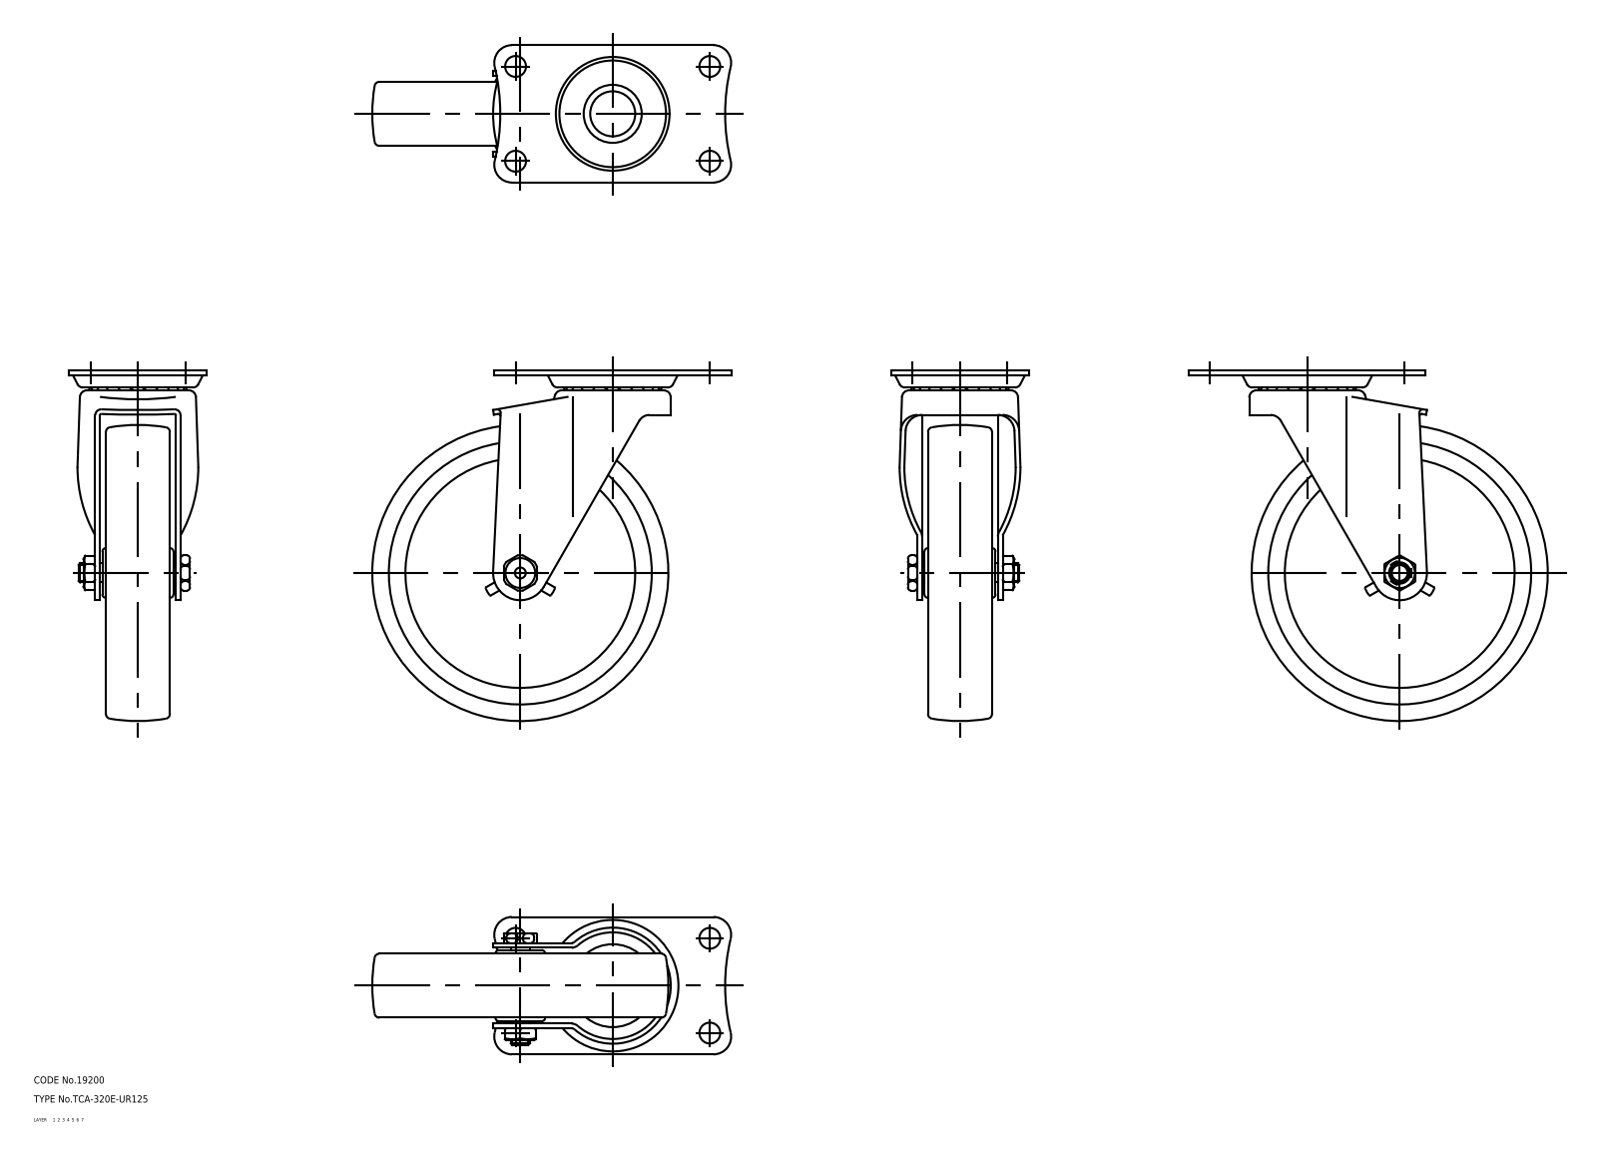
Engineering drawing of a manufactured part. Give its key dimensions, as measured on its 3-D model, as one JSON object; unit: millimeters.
{"part_name": "wheel; mounting plate; main shaft; axle (+1 more)", "step_written_by": "CADfix (AUTOMOTIVE_DESIGN)", "units": "millimeters", "bodies": {"solids": 5, "faces": 372, "planar": 0, "cylindrical": 0, "other": 372}, "overall_size": [151.5, 148, 58], "volume_mm3": 285428, "surface_area_mm2": 78086}
